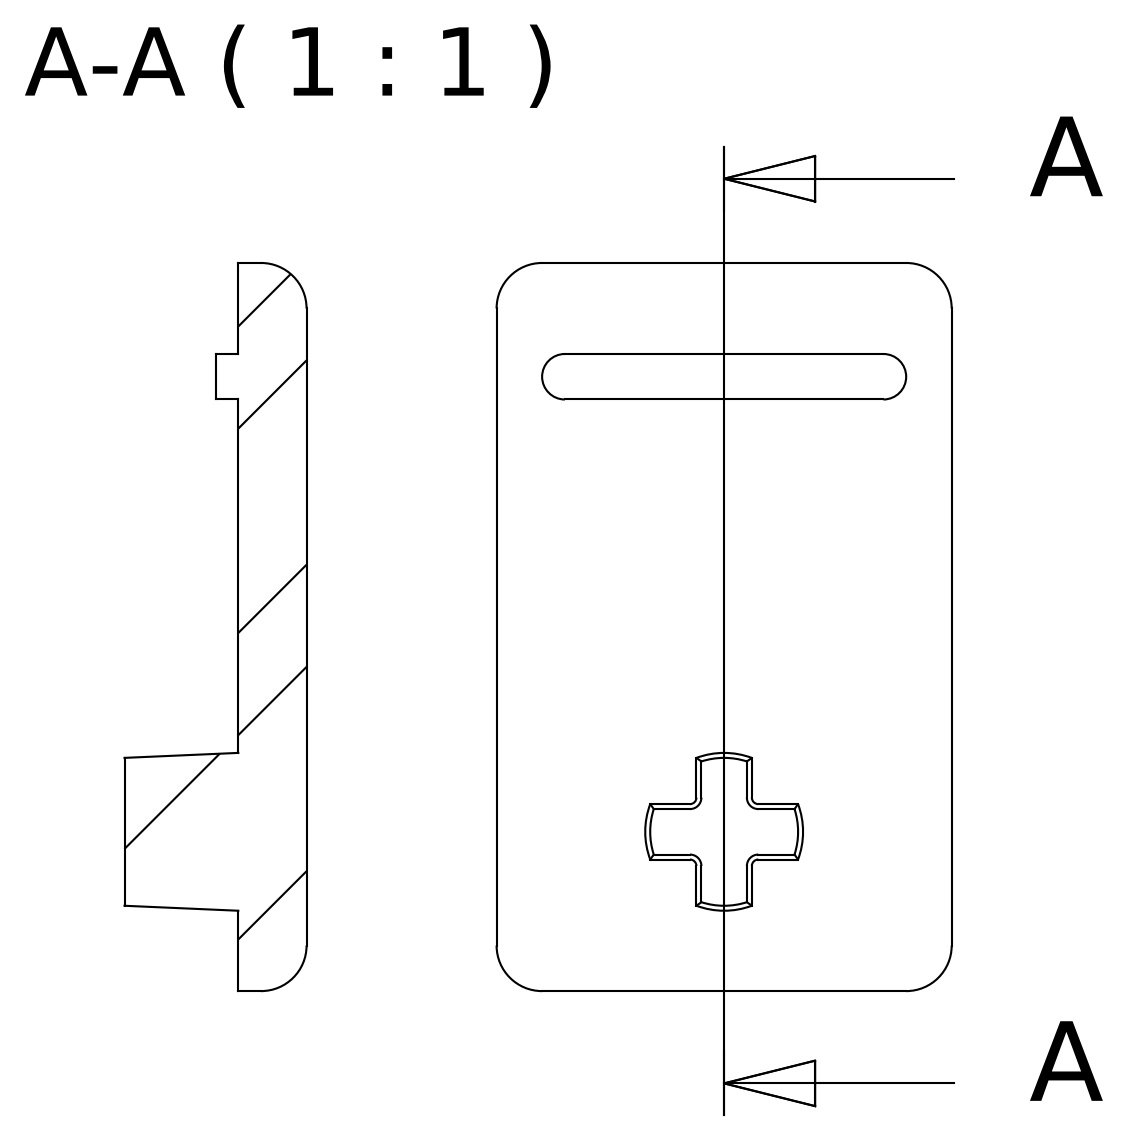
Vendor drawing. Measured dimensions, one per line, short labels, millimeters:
name: DTPTR0000016
written by: Autodesk Inventor 2016 (AUTOMOTIVE_DESIGN)
unit: mm
bodies: 1 solid, 40 faces (18 planar, 10 cylindrical, 12 other)
size: 32 × 20 × 8
volume: 1 979 mm³; area: 1 640 mm²
rounds: 8× R2, 2× R1
face distances: 3, 4, 1, 20, 5, 8, 32, 26, 28, 2
